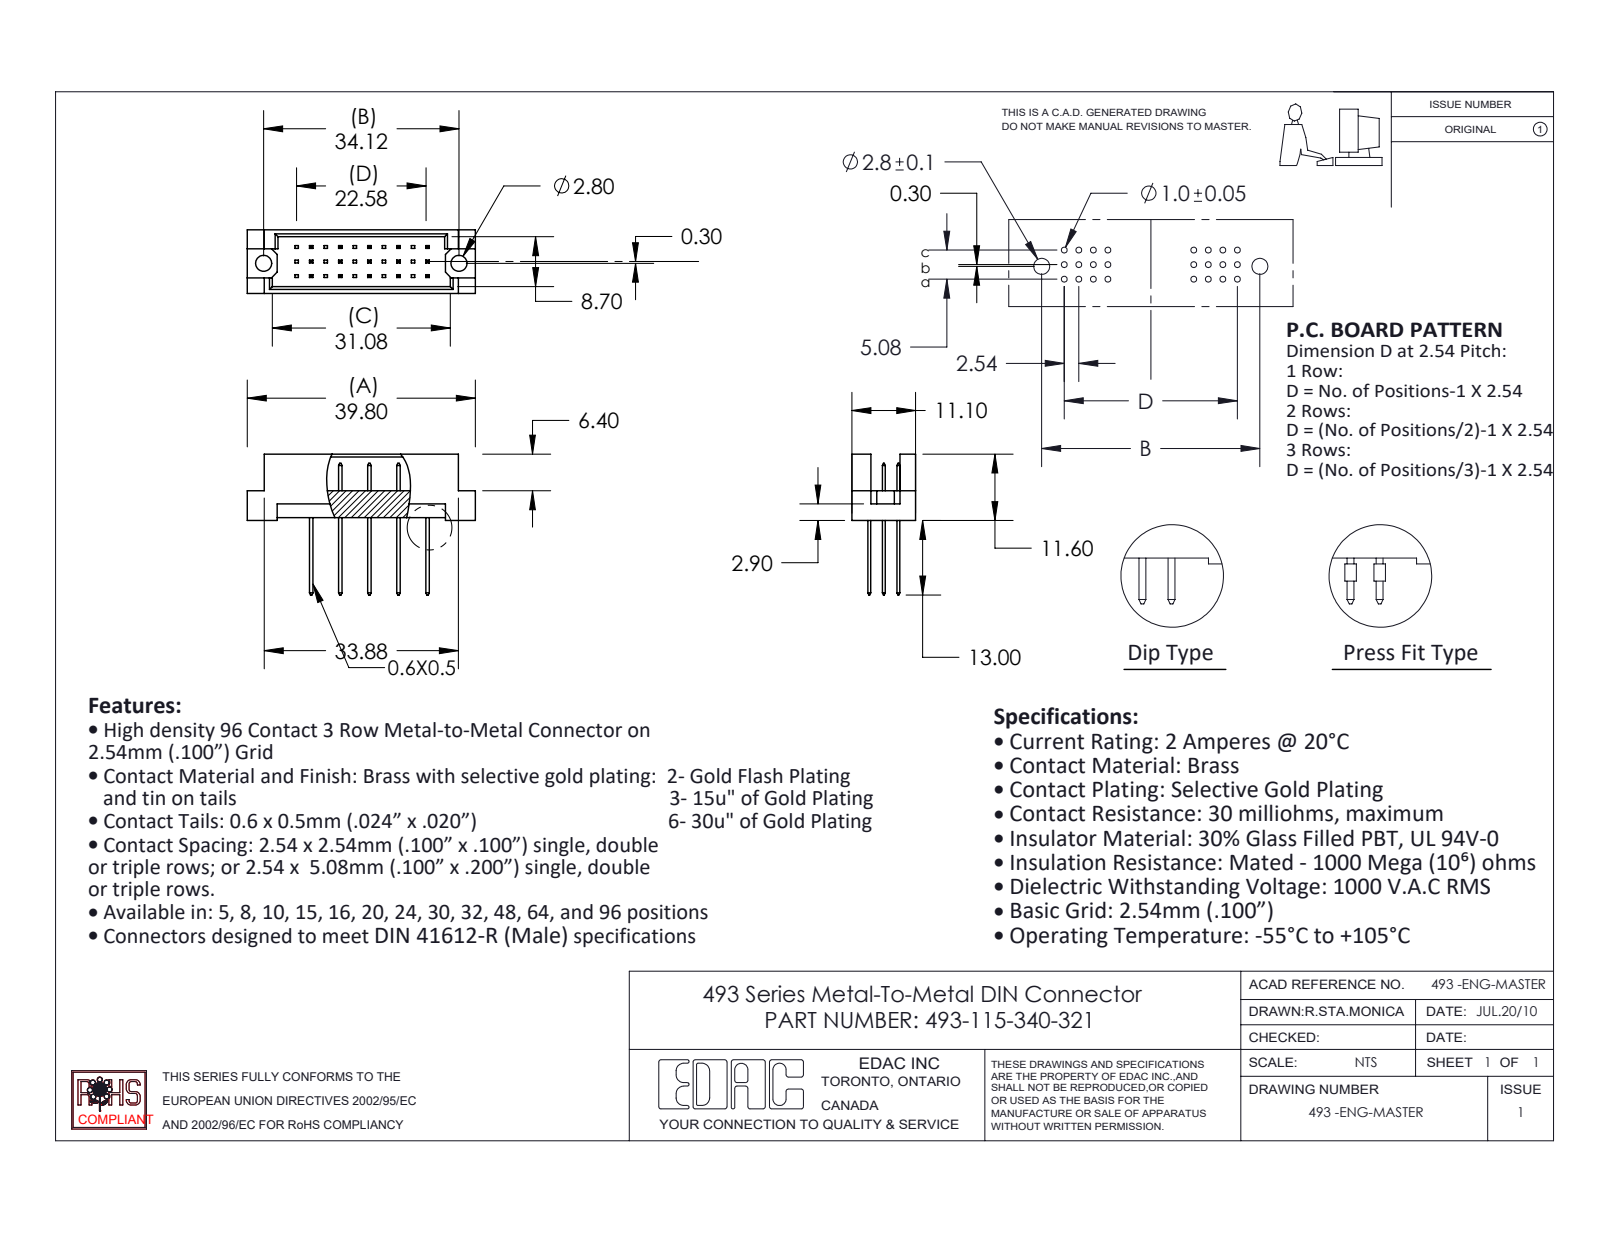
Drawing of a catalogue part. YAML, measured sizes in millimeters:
part_name: "493-290_40; 493-115-340-322; 493 Part_30"
step_written_by: "SolidWorks 2020 (CONFIG_CONTROL_DESIGN)"
units: millimeters
bodies: {solids: 16, faces: 382, planar: 378, cylindrical: 4, other: 0}
overall_size: [39.8, 24.6, 11.1]
volume: 2475
surface_area: 3491
round_holes:
  - {diameter: 2.8, count: 2}
face_to_face_distances: [5.08, 1.2, 9.9, 11.1, 0.5, 2.54, 8.7, 4.7, 10.16, 0.6]
hole_center_spacings: [34.12]
